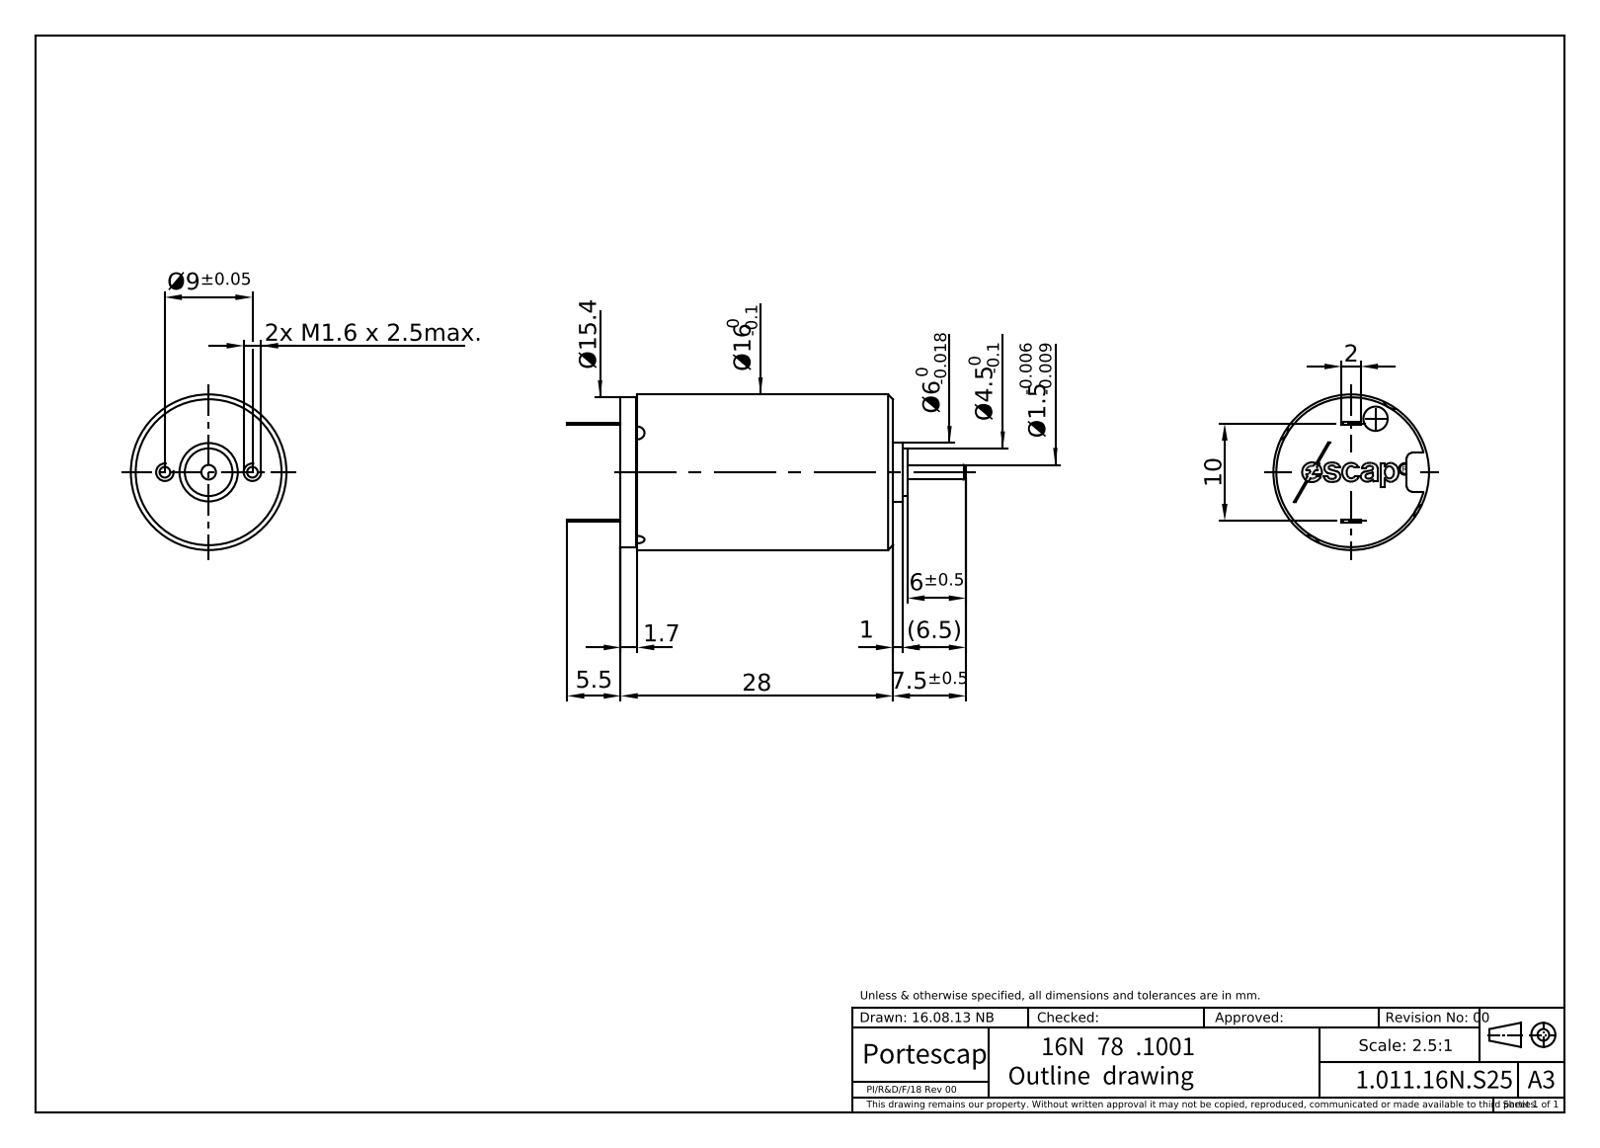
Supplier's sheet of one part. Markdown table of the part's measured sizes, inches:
| quantity | value |
| --- | --- |
| part name | 16N_28_235_B16_200_27_ASM |
| STEP written by | PRO/ENGINEER BY PARAMETRIC TECHNOLOGY CORPORATION, 2014310 (CONFIG_CONTROL_DESIGN) |
| units | inches |
| bodies | 1 solid, 189 faces (103 planar, 54 cylindrical, 32 other) |
| overall size | 1.614 × 0.63 × 0.63 |
| volume | 0.337 in³ |
| surface area | 3.522 in² |
| round holes (diameter × count) | 0.049 × 2, 0.059 × 1, 0.071 × 1, 0.087 × 1, 0.098 × 1, 0.11 × 1 |
| round bosses / shafts (diameter × count) | 0.63 × 1, 0.606 × 1, 0.604 × 1, 0.425 × 1, 0.236 × 1, 0.177 × 1, 0.059 × 1 |
| partial cylindrical surfaces (radius × count) | 0.02 × 6, 0.024 × 2, 0.055 × 2, 0.028 × 1, 0.287 × 1, 0.289 × 1 |
| main face-to-face distances | 1.102, 0.028, 1.075, 0.039, 0.024, 0.035, 0.02, 0.063, 1.039, 1.063 |
| hole center spacings | 0.177, 0.354, 0.028, 0.075, 0.15, 0.158, 0.185, 0.23 |
